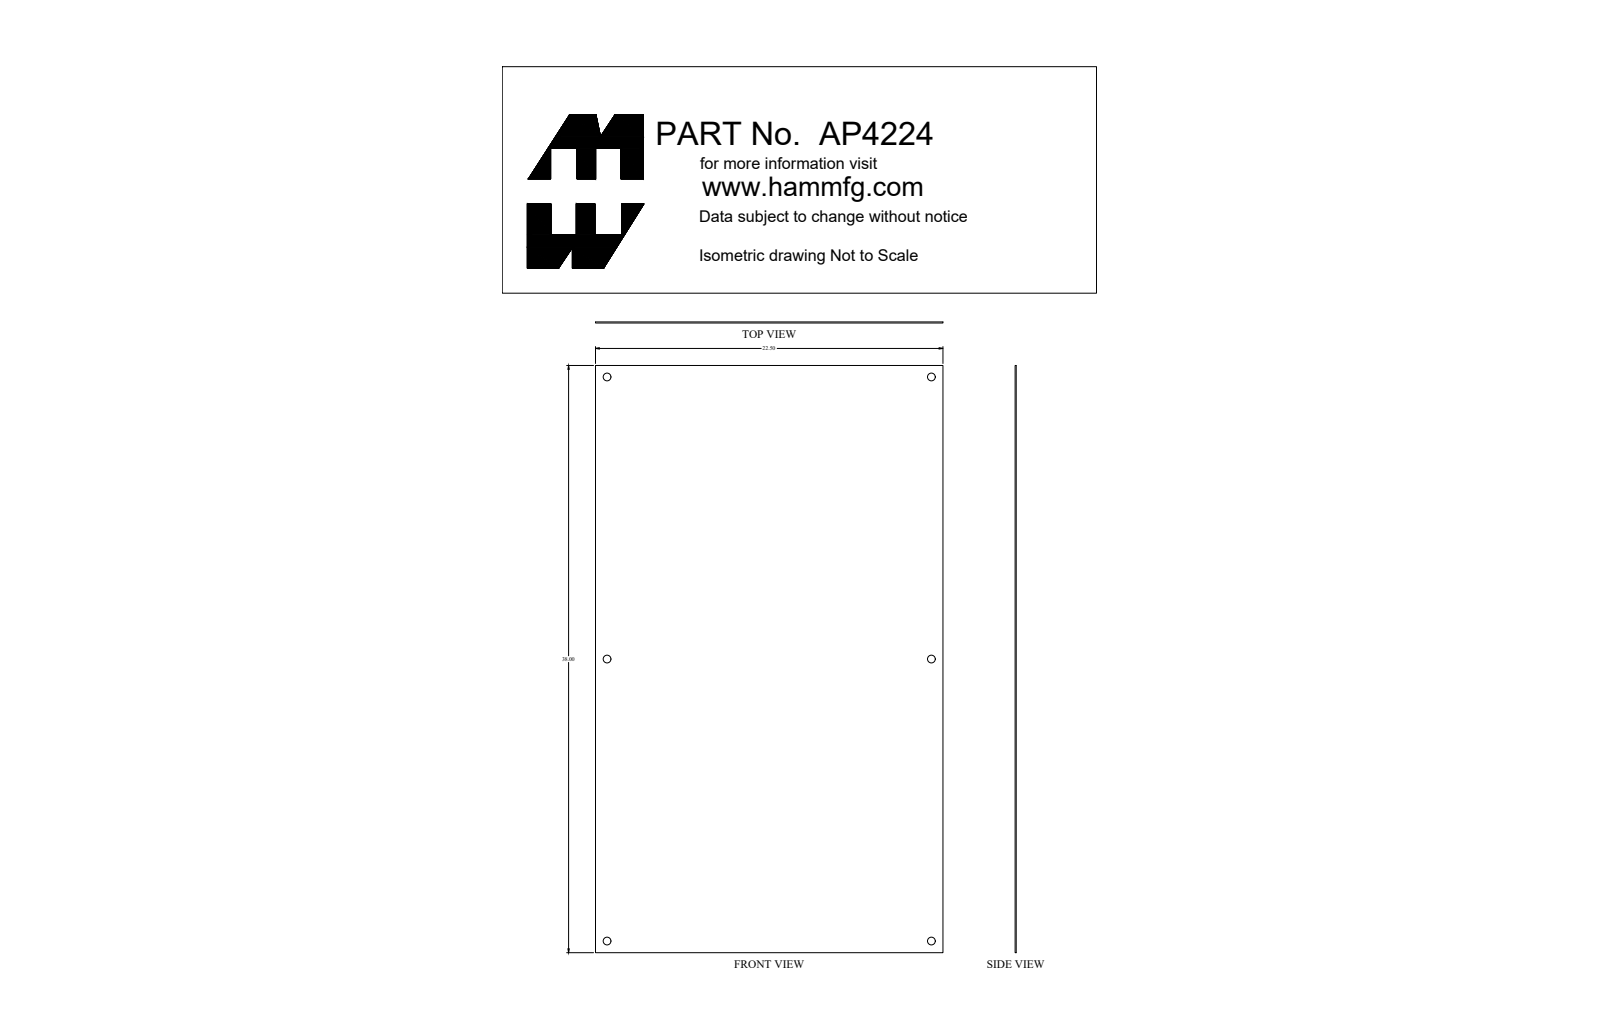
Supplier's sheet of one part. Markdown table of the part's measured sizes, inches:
| quantity | value |
| --- | --- |
| part name | AP4224_Default |
| STEP written by | SolidWorks 2019 (CONFIG_CONTROL_DESIGN) |
| units | inches |
| bodies | 1 solid, 18 faces (6 planar, 12 cylindrical, 0 other) |
| overall size | 38 × 22.5 × 0.072 |
| volume | 61.48 in³ |
| surface area | 1 717 in² |
| round holes (diameter × count) | 0.5 × 6 |
| main face-to-face distances | 0.072, 22.5, 38 |
| hole center spacings | 18.25, 27.822, 21, 36.5, 42.11 |
